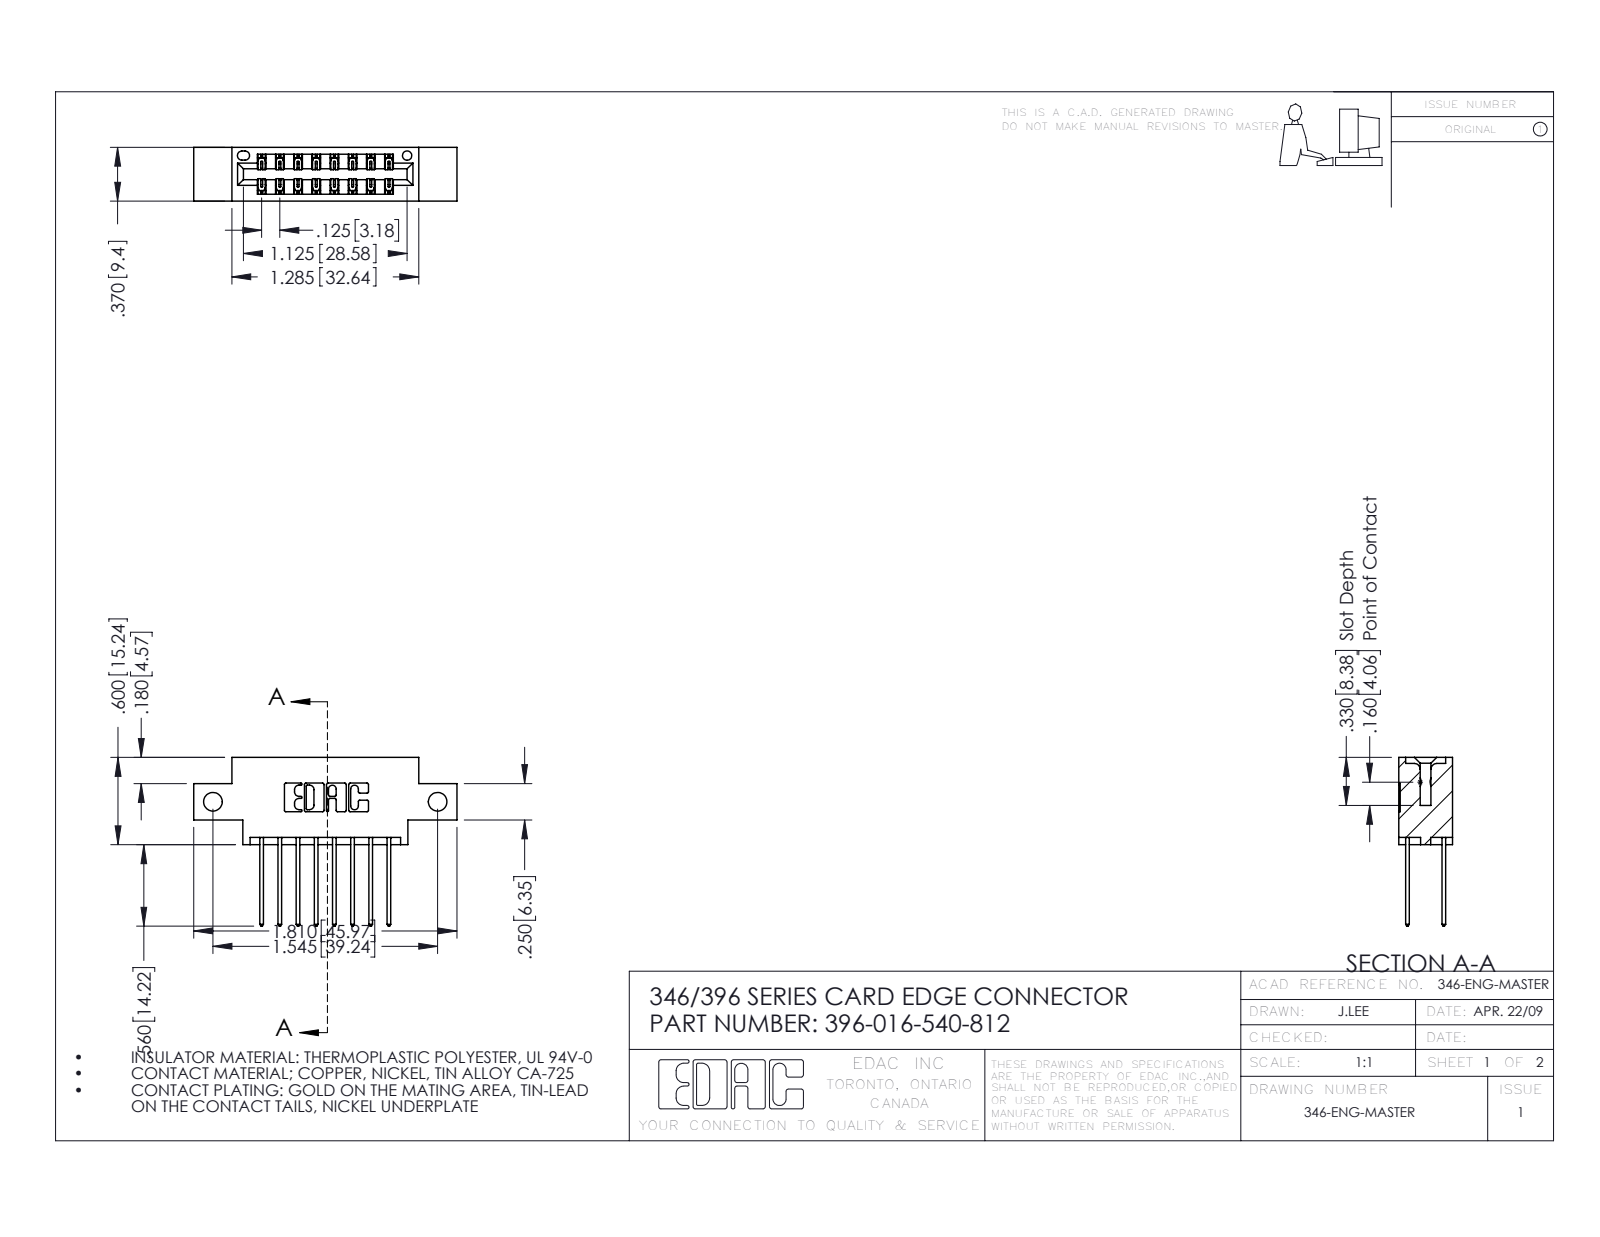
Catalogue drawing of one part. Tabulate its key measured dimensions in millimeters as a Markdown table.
| quantity | value |
| --- | --- |
| part name | 396-016-540-812; 346 Part_0.170 Offset - Side Mount; 345-292-001_345-293-140 |
| STEP written by | SolidWorks 2016 (CONFIG_CONTROL_DESIGN) |
| units | millimeters |
| bodies | 17 solids, 958 faces (640 planar, 318 cylindrical, 0 other) |
| overall size | 46 × 29.5 × 9.4 |
| volume | 4 030 mm³ |
| surface area | 5 345 mm² |
| round holes (diameter × count) | 3.3 × 2, 1.6 × 1 |
| partial cylindrical surfaces (radius × count) | 0.2 × 24, 0.3 × 22, 0.3 × 16, 0.2 × 6, 0.8 × 6, 0.7 × 3, 0.4 × 2, 0.6 × 2 |
| main face-to-face distances | 6.4, 1.2, 8.2, 9.4, 1.8, 7.6, 0.6, 7, 3.8, 5.6 |
| hole center spacings | 39.2 |
